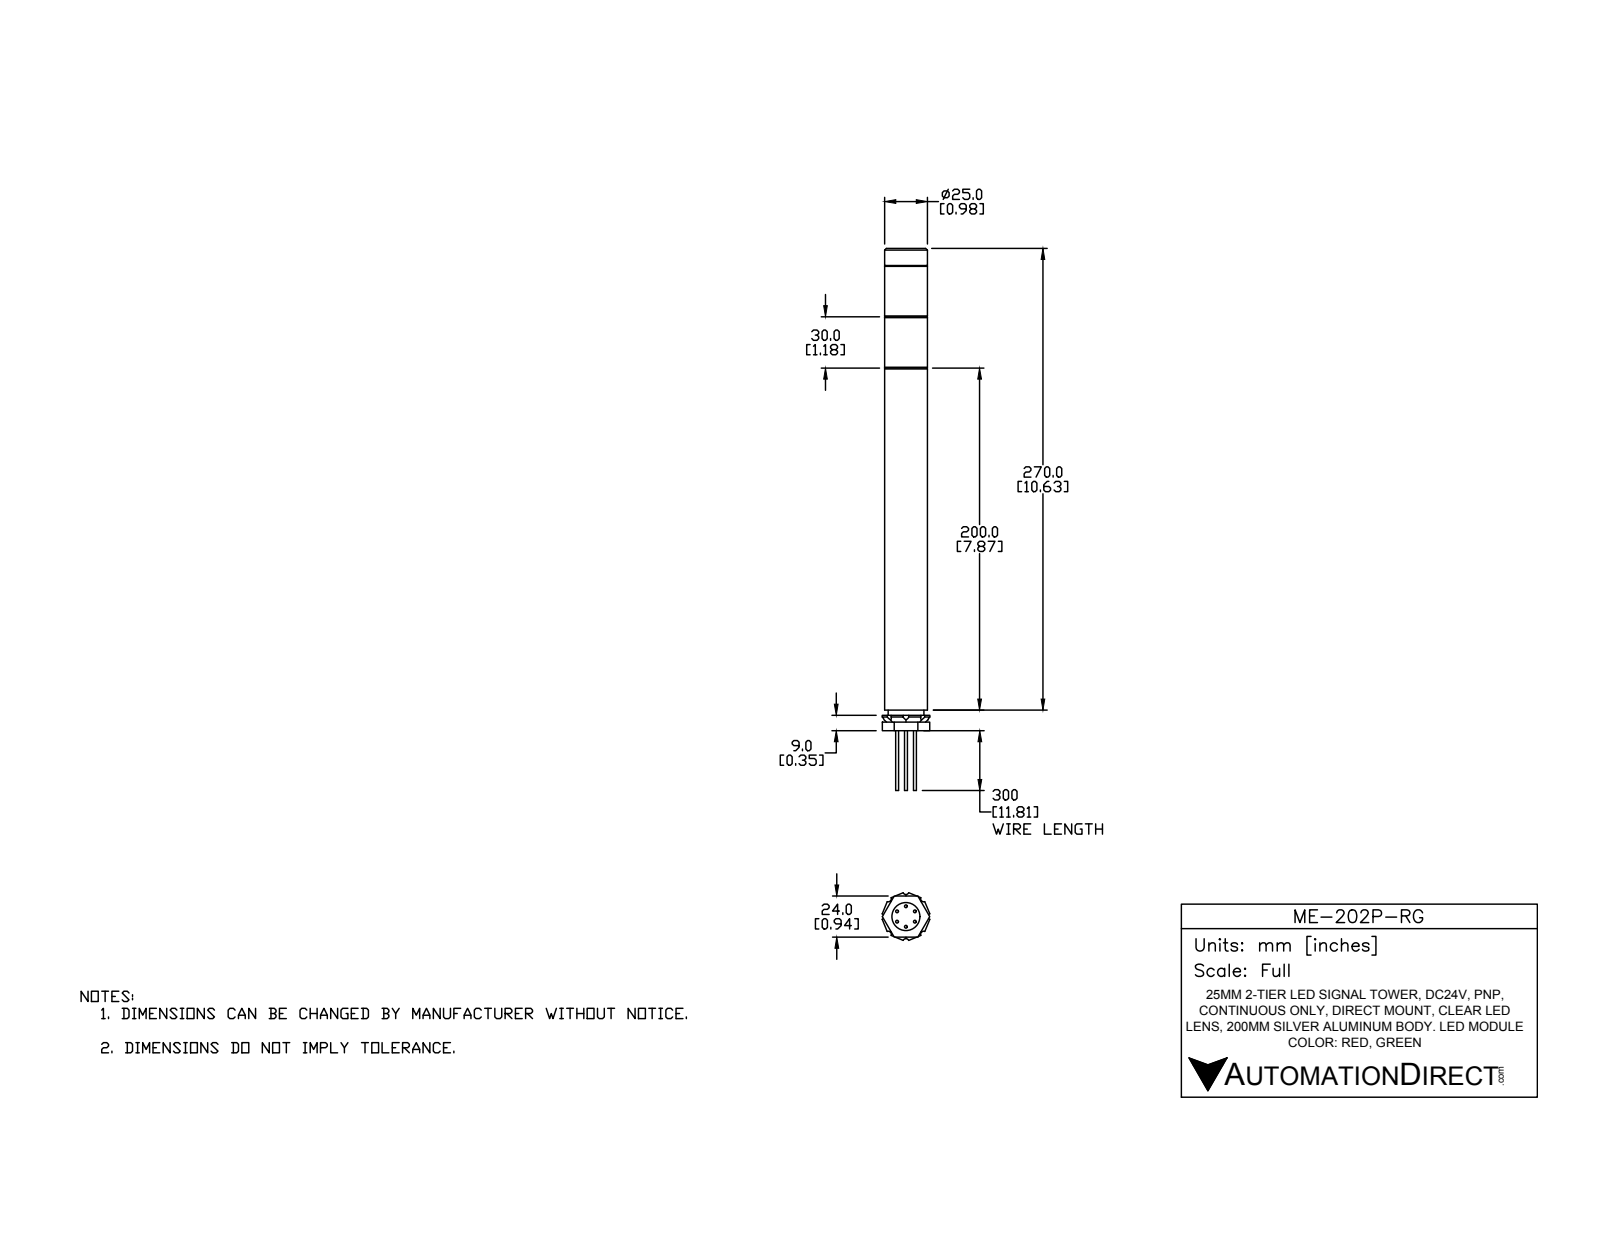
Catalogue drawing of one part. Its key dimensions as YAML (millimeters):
part_name: "ME-202P-RG"
step_written_by: "SolidWorks 2016 (AUTOMOTIVE_DESIGN)"
units: millimeters
bodies: {solids: 13, faces: 140, planar: 73, cylindrical: 49, other: 18}
overall_size: [317, 27.89, 27.89]
volume: 126899
surface_area: 34535
round_holes:
  - {diameter: 3.2, count: 1}
  - {diameter: 7.7, count: 1}
  - {diameter: 16.4, count: 1}
  - {diameter: 18, count: 1}
  - {diameter: 20.7, count: 1}
  - {diameter: 21, count: 1}
round_bosses_or_shafts:
  - {diameter: 1.7, count: 6}
  - {diameter: 25, count: 1}
  - {diameter: 20.9, count: 1}
  - {diameter: 16, count: 1}
  - {diameter: 5, count: 1}
partial_cylinders:
  - {radius: 1.75, count: 8}
face_to_face_distances: [30, 60, 40, 237, 167, 197, 227, 70, 10, 45]
